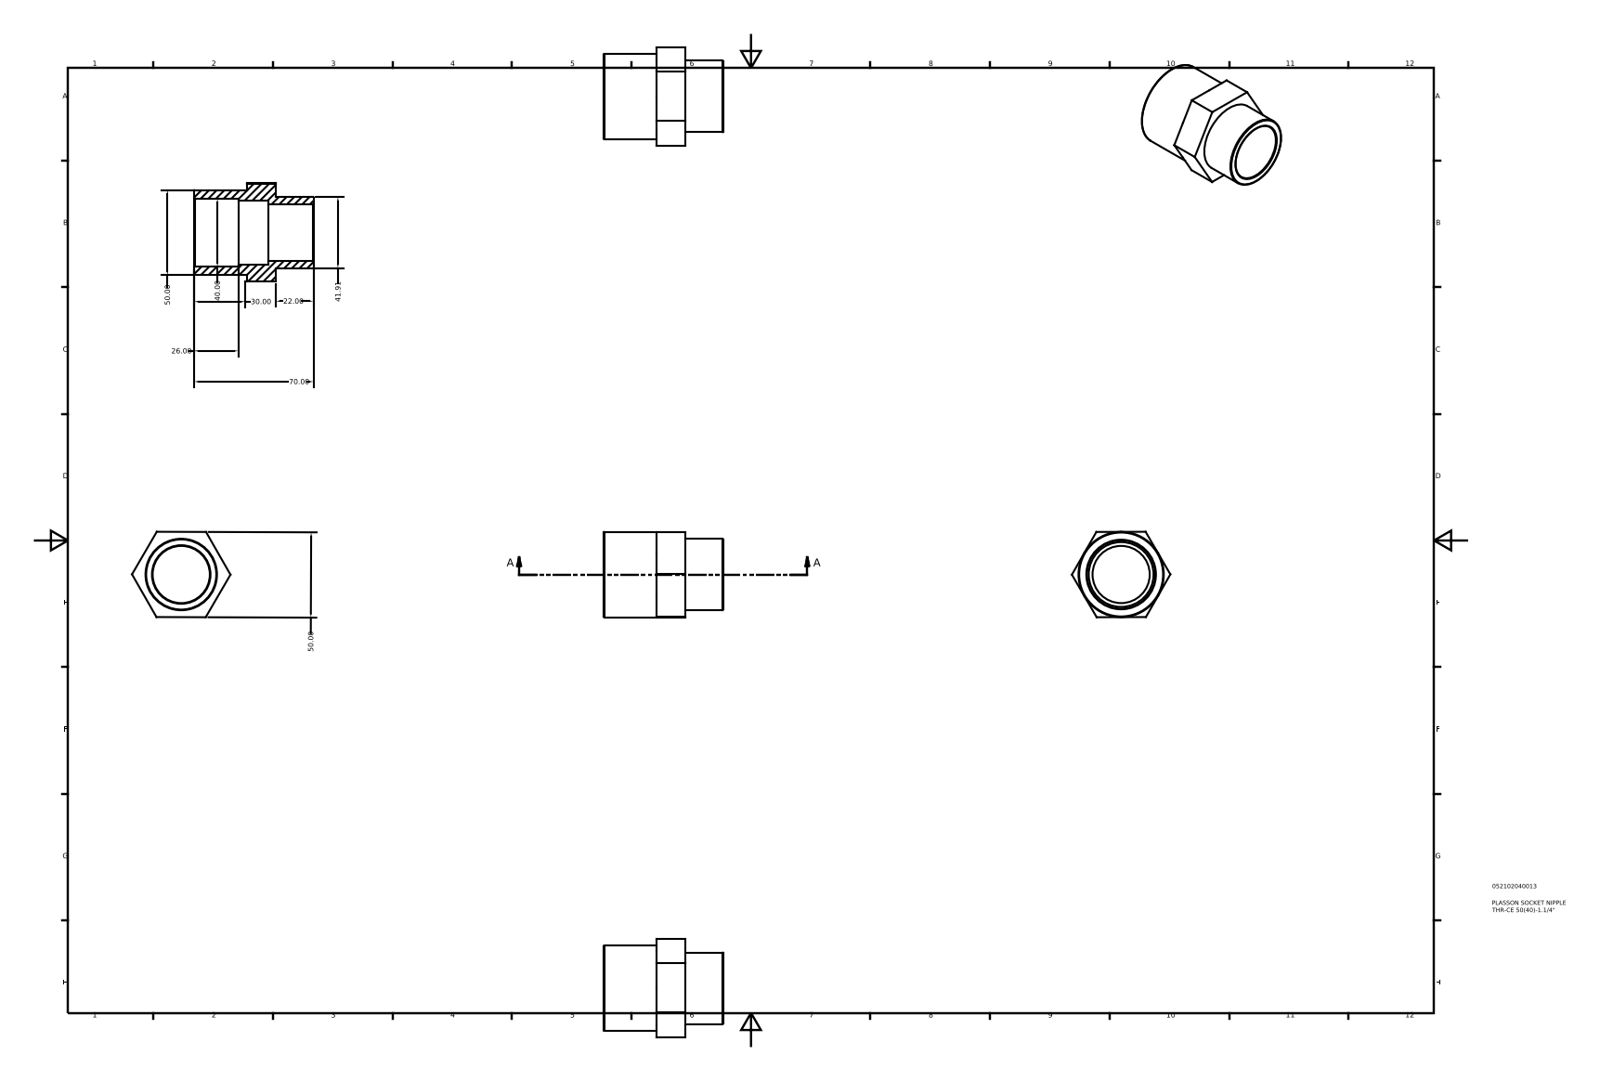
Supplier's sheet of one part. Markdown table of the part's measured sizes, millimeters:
| quantity | value |
| --- | --- |
| part name | 052102040013 |
| STEP written by | Autodesk Inventor 2015 (AUTOMOTIVE_DESIGN) |
| units | millimeters |
| bodies | 1 solid, 26 faces (17 planar, 5 cylindrical, 4 other) |
| overall size | 70 × 57.73 × 50.1 |
| volume | 52 065 mm³ |
| surface area | 21 335 mm² |
| round holes (diameter × count) | 33.53 × 1, 38 × 1, 40 × 1 |
| round bosses / shafts (diameter × count) | 50 × 1, 41.91 × 1 |
| main face-to-face distances | 48, 22, 49.98, 50, 50.01, 70, 43.6, 4.4, 26.4, 31 |
